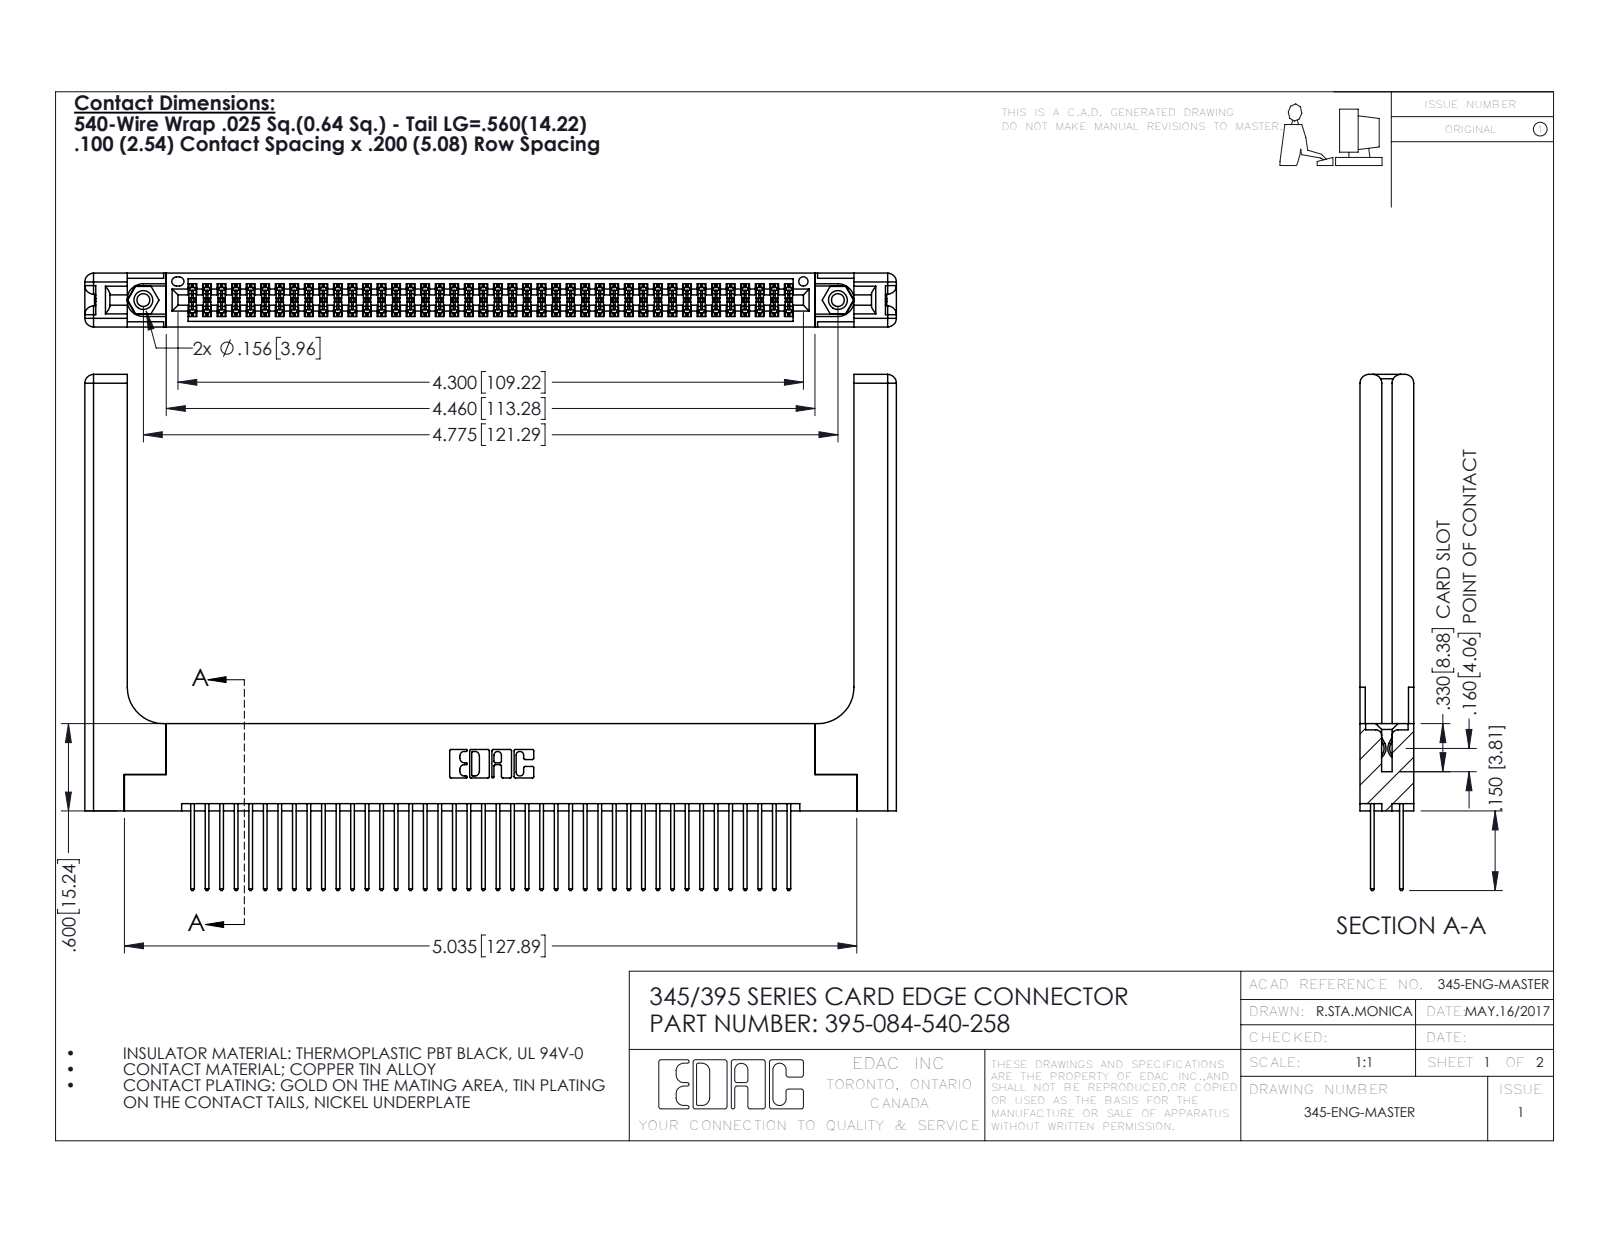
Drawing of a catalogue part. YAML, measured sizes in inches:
part_name: "345-292-001_345-293-140; 345-220-058_345-220-058; 395-084-540-258; 345 Part_Flush Mounting Lugs - 0.156 Dia-TH (+1 more)"
step_written_by: "SolidWorks 2016 (CONFIG_CONTROL_DESIGN)"
units: inches
bodies: {solids: 89, faces: 4582, planar: 3000, cylindrical: 1522, other: 60}
overall_size: [5.579, 3.547, 0.37]
volume: 1.377
surface_area: 42.4
round_holes:
  - {diameter: 0.089, count: 2}
  - {diameter: 0.125, count: 2}
  - {diameter: 0.156, count: 2}
  - {diameter: 0.064, count: 1}
round_bosses_or_shafts:
  - {diameter: 0.155, count: 2}
partial_cylinders:
  - {radius: 0.006, count: 126}
  - {radius: 0.01, count: 84}
  - {radius: 0.01, count: 22}
  - {radius: 0.06, count: 16}
  - {radius: 0.007, count: 6}
  - {radius: 0.031, count: 6}
  - {radius: 0.026, count: 3}
  - {radius: 0.014, count: 2}
face_to_face_distances: [0.072, 0.298, 0.37, 0.2, 0.098, 0.272, 0.025, 0.225, 0.175, 0.148]
hole_center_spacings: [0.27, 4.539, 4.775]
